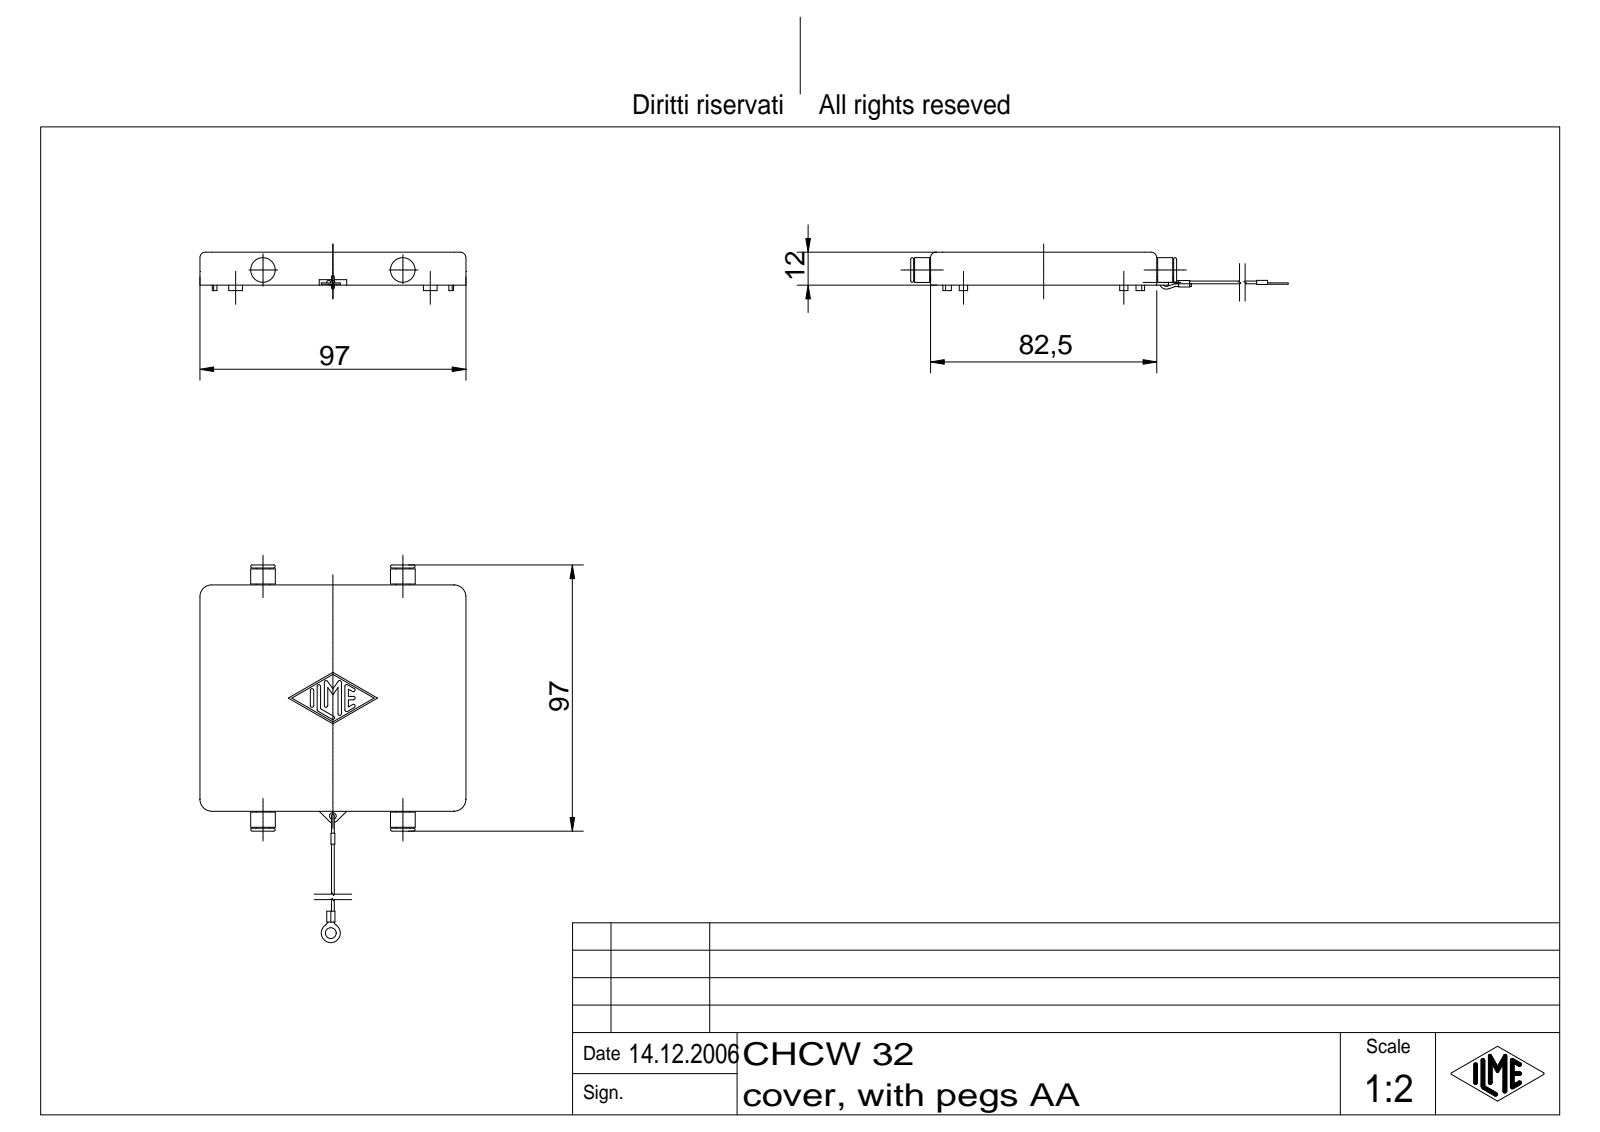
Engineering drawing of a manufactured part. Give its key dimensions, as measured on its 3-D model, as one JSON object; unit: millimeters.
{"part_name": "CHCW 32", "step_written_by": "Autodesk Inventor 7 (AUTOMOTIVE_DESIGN)", "units": "millimeters", "bodies": {"solids": 2, "faces": 258, "planar": 99, "cylindrical": 81, "other": 78}, "overall_size": [214, 97, 14], "volume_mm3": 39860, "surface_area_mm2": 25218, "round_holes": [[2.5, 1], [4, 1]], "round_bosses_or_shafts": [[1, 4], [9, 2], [5, 2], [7, 1]], "partial_cylinders_radius": [[0.62, 14], [2, 8], [0.7, 4], [4.3, 4], [0.75, 2], [1, 2], [3, 2], [1.75, 1]], "face_to_face_distances": [3, 4.5, 9, 12, 78, 92.5, 82.5, 97, 73.5, 88], "hole_center_spacings": [119]}
